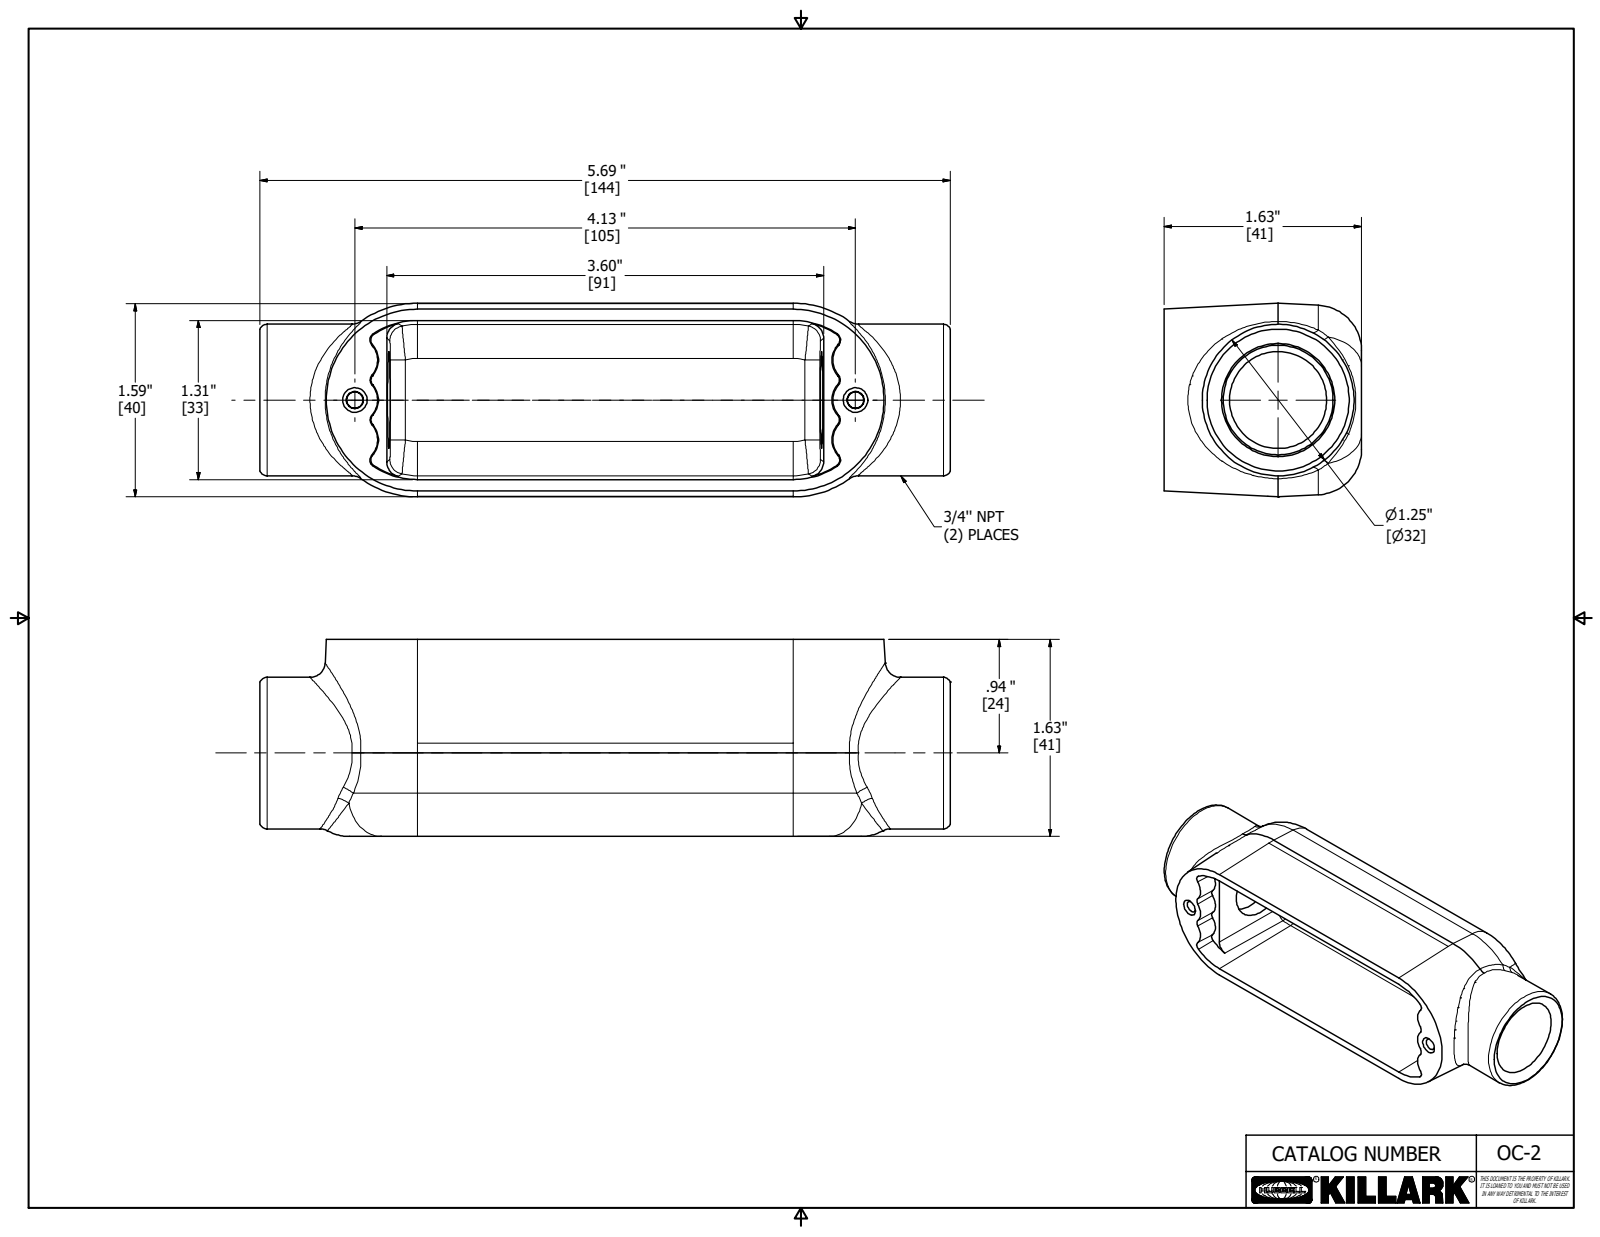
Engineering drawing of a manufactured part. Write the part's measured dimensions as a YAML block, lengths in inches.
part_name: "18258-1"
step_written_by: "Autodesk Inventor 2018 (AUTOMOTIVE_DESIGN)"
units: inches
bodies: {solids: 1, faces: 120, planar: 38, cylindrical: 14, other: 68}
overall_size: [5.688, 1.625, 1.598]
volume: 3.929
surface_area: 51.19
round_holes:
  - {diameter: 0.8, count: 1}
round_bosses_or_shafts:
  - {diameter: 1.25, count: 1}
partial_cylinders:
  - {radius: 0.031, count: 4}
  - {radius: 0.125, count: 2}
  - {radius: 0.281, count: 2}
  - {radius: 0.375, count: 2}
face_to_face_distances: [1.596, 0.125, 1.625, 1.5, 0.031, 0.094, 1.531, 0.063, 1.594, 1.375]
